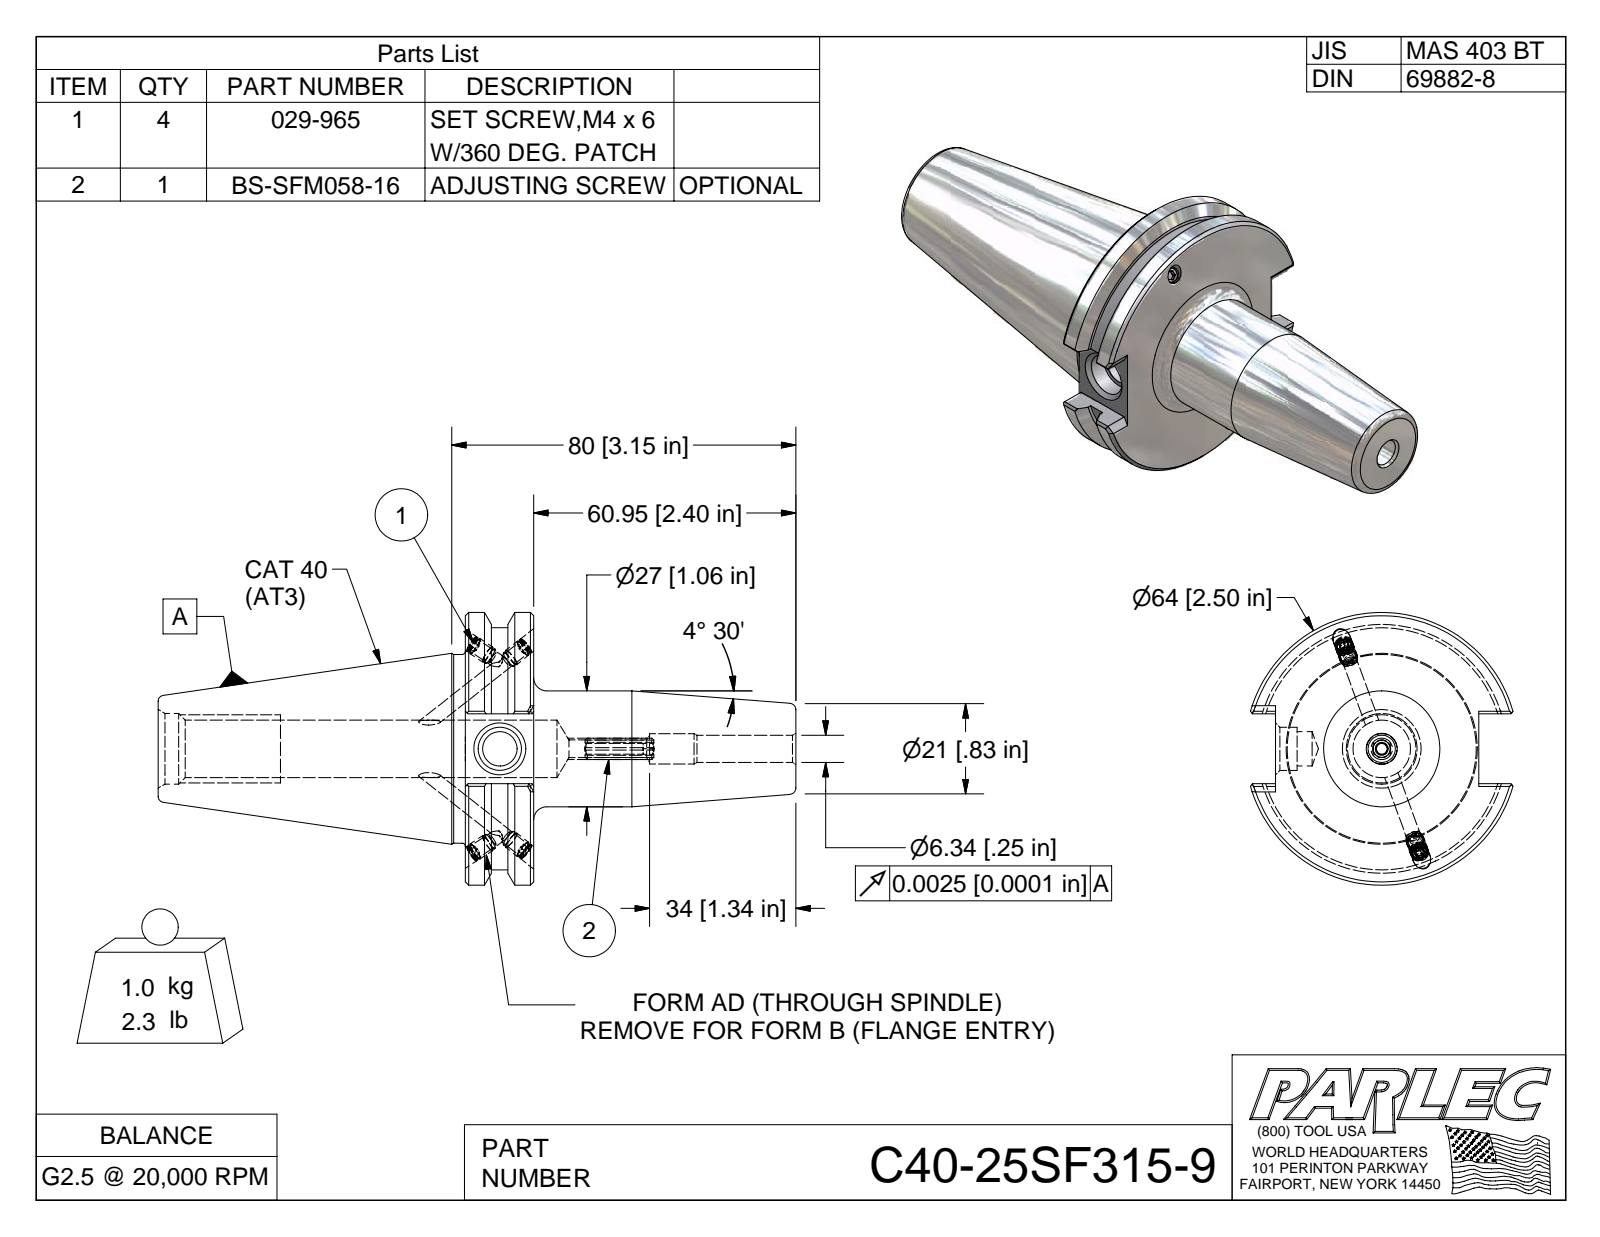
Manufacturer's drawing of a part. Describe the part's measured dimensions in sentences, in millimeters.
The part is named "C40-25SF315-9; C40BC-25SF315-9-1; 029-965; BS-SFM058-16". Its 3-D file was written by "Autodesk Inventor 2009 (AUTOMOTIVE_DESIGN)". It is 6 solids with 172 faces: 87 planar, 32 cylindrical and 53 other. Overall it measures 148.3 by 63.5 by 61 millimeters. Its volume is 128 300 cubic millimeters and its surface area 27 690 square millimeters. Round holes: 4 of diameter 3.3, 4 of diameter 4.1, 1 of diameter 6.4, 1 of diameter 7.1. Round bosses or shafts: 4 of diameter 4.2, 4 of diameter 4, 1 of diameter 63.5, 1 of diameter 56.4, 1 of diameter 43.9, 1 of diameter 27. Partial cylindrical surfaces (rounded edges, fillets, slot ends): 1 of radius 2.5. The main face-to-face distances are 15.9, 76.8, 61, 16.3, 47.2, 71.4, 87.3, 148.3, 81.3, 9.9.
